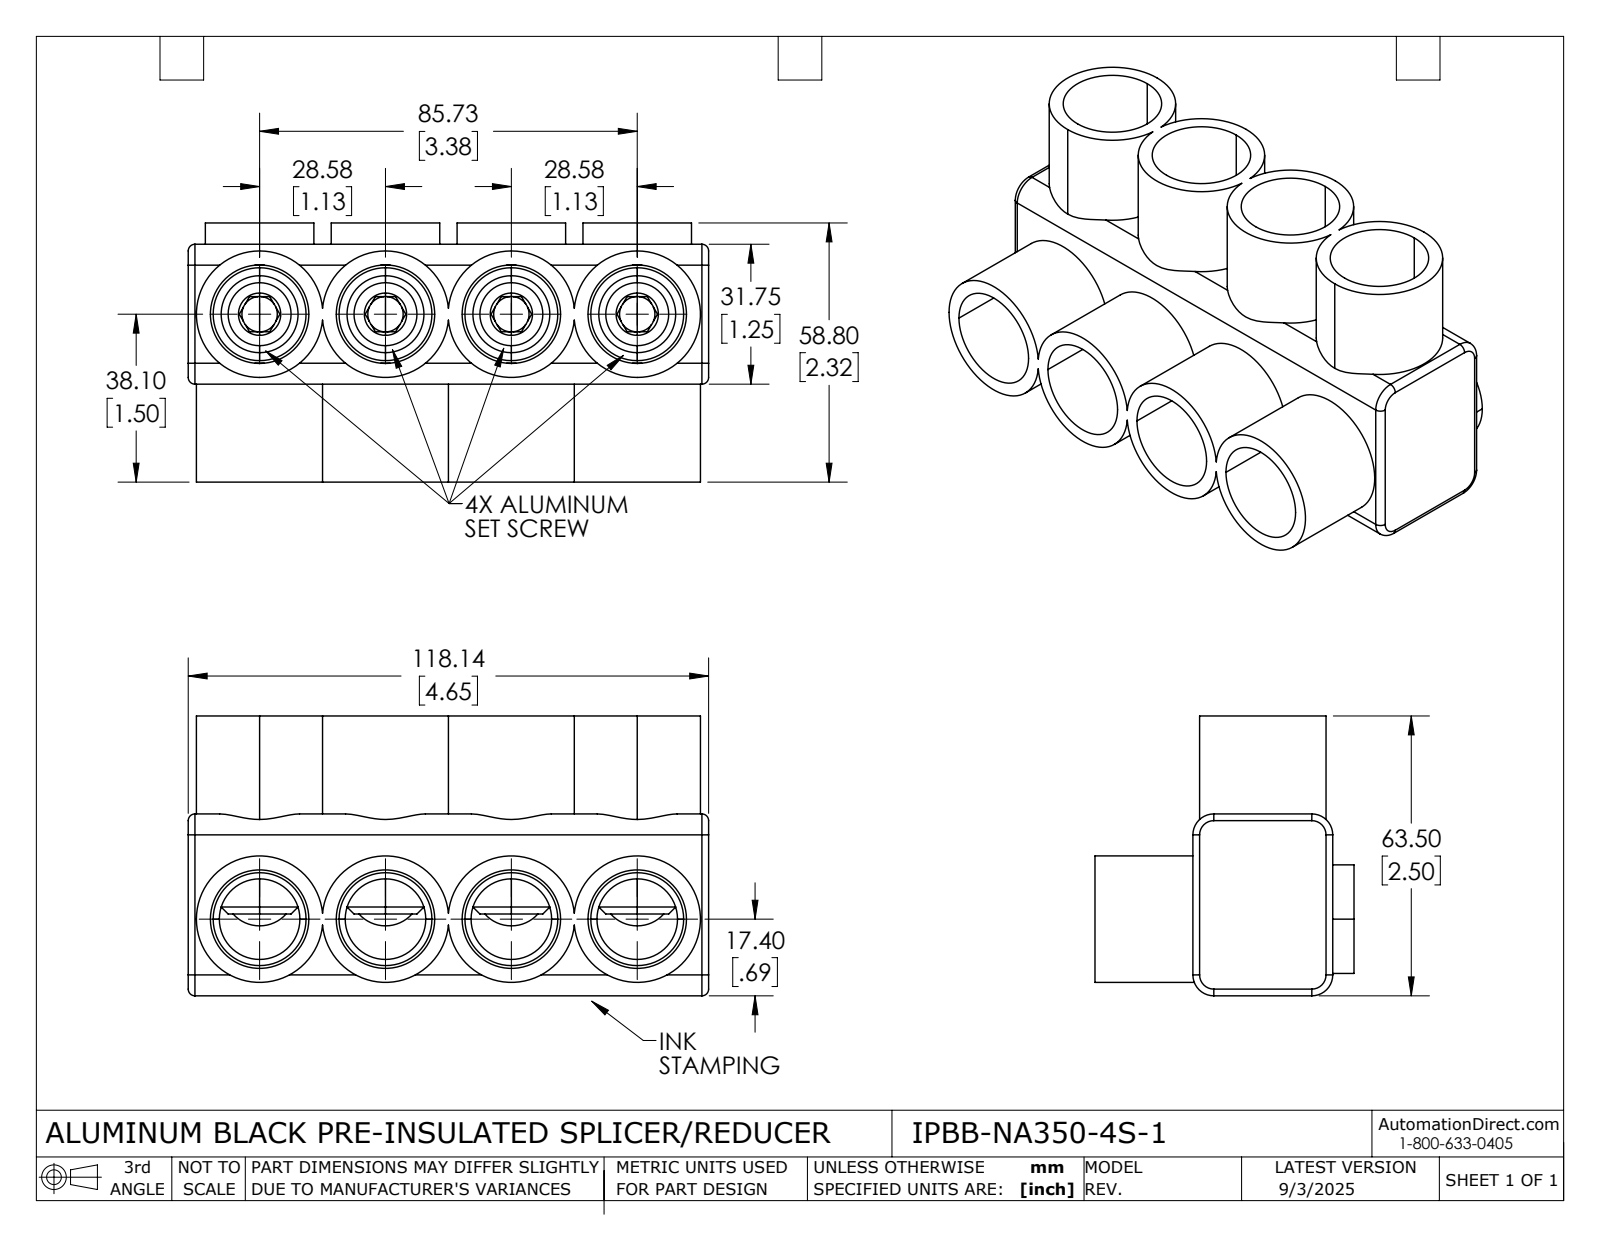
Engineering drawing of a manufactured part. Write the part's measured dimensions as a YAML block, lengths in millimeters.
part_name: "IPBB-NA350-4S-1"
step_written_by: "SolidWorks 2024 (AUTOMOTIVE_DESIGN)"
units: millimeters
bodies: {solids: 6, faces: 313, planar: 130, cylindrical: 111, other: 72}
overall_size: [118.1, 63.5, 58.8]
volume: 170400
surface_area: 85810
round_holes:
  - {diameter: 22.4, count: 8}
  - {diameter: 8, count: 4}
  - {diameter: 15.9, count: 4}
  - {diameter: 18.3, count: 4}
round_bosses_or_shafts:
  - {diameter: 28.7, count: 8}
  - {diameter: 24.6, count: 4}
  - {diameter: 17.4, count: 4}
partial_cylinders:
  - {radius: 1.5, count: 8}
  - {radius: 1.6, count: 4}
  - {radius: 4.7, count: 4}
face_to_face_distances: [3.2, 25.4, 28.6, 38.1, 34.9, 115, 8, 33.4, 111.8, 4.8]
hole_center_spacings: [28.6, 57.2, 28.6, 85.7]
